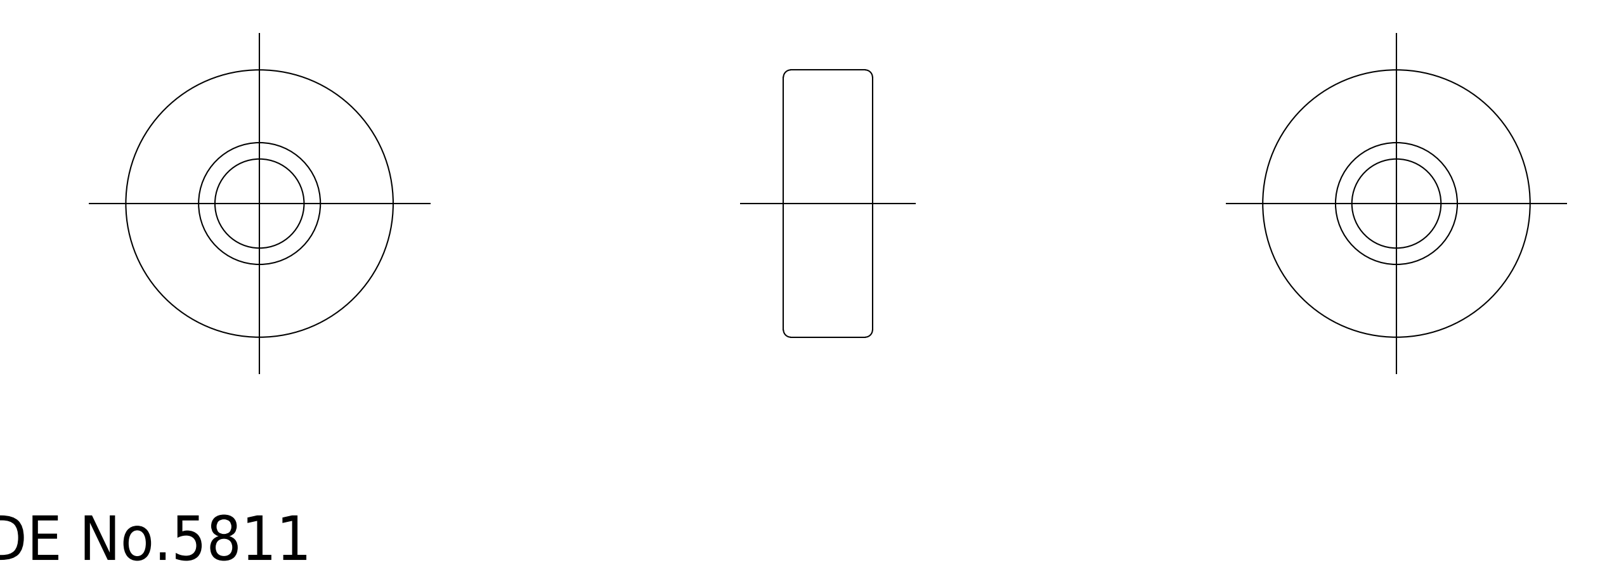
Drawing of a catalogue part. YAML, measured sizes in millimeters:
part_name: "roller"
step_written_by: "CADfix (AUTOMOTIVE_DESIGN)"
units: millimeters
bodies: {solids: 1, faces: 28, planar: 0, cylindrical: 0, other: 28}
overall_size: [18, 18, 6]
volume: 1353
surface_area: 1256
